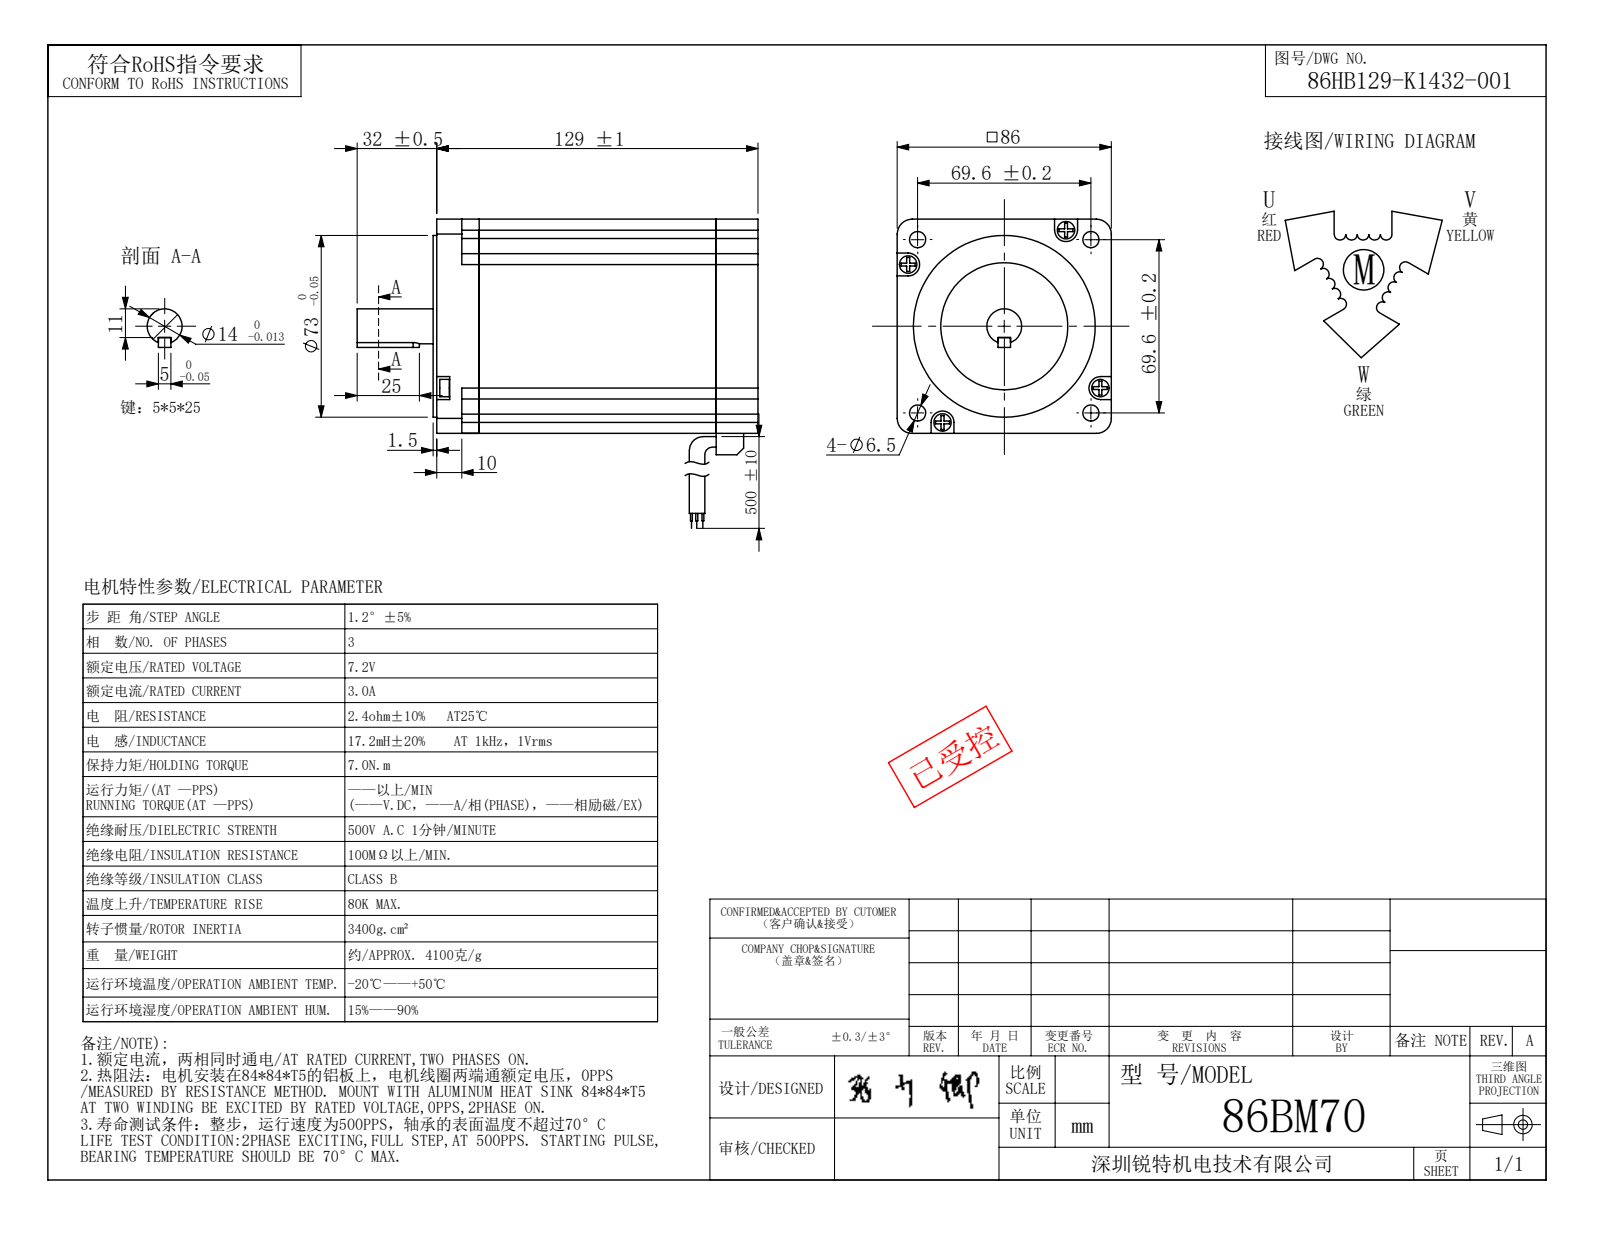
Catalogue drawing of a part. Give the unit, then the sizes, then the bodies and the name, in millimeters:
Units: millimetres
Overall size (bounding box): 161 × 86 × 86
Round holes (diameter × count): ⌀4.4 ×8, ⌀6.5 ×4, ⌀40 ×1, ⌀51 ×1, ⌀80.8 ×1
Round bosses / shafts (diameter × count): ⌀7 ×4, ⌀73 ×1, ⌀52 ×1, ⌀14 ×1
Partial cylindrical surfaces — rounded edges, fillets, slot ends (radius × count): R4.4 ×9, R4.6 ×4, R6 ×4, R6.05 ×4, R2.5 ×1, R4.41 ×1
Main face-to-face distances: 86, 17, 112, 129, 119, 102, 10, 13.8, 72.2, 95
Hole centre spacings: 10.7, 45.88, 59.72, 64.88, 74.08, 94.55, 19.52, 49.21
Volume: 351 286 mm³ · Surface area: 111 080 mm²
Bodies: 8 solids, 277 faces (145 planar, 124 cylindrical, 8 other)
Part name (STEP PRODUCT): 86BM70(86HB129-K1432-001)
STEP written by: SolidWorks 2020 (AUTOMOTIVE_DESIGN)
